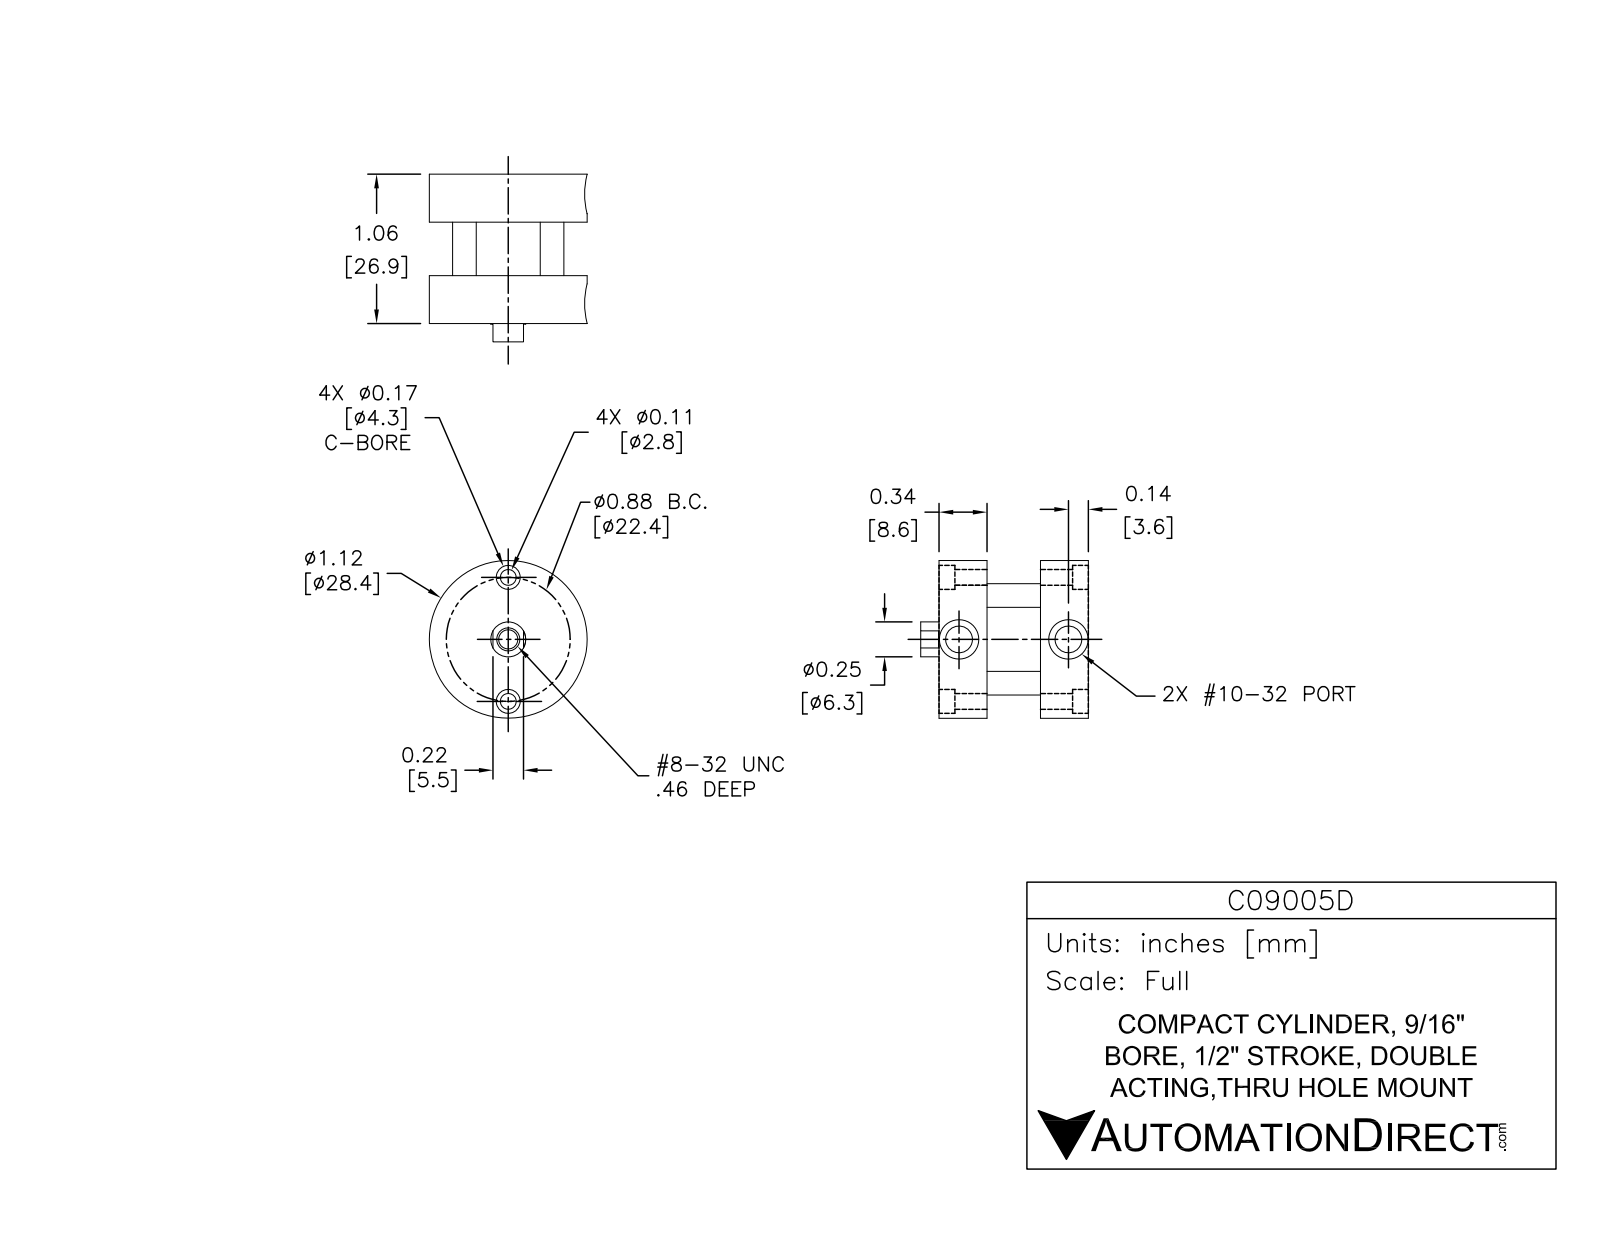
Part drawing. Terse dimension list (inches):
name: C09005D-FO1_BM_heads (2); C09005D-FO1_BM_tube; C09005D-FO1_BM_heads; C09005D-FO1_BM_r (+3 more)
written by: SolidWorks 2014 (AUTOMOTIVE_DESIGN)
unit: in
bodies: 9 solids, 145 faces (47 planar, 88 cylindrical, 10 other)
size: 1.19 × 1.12 × 1.12
volume: 0.713 in³; area: 13.56 in²
holes: 6× ⌀0.12, 2× ⌀0.156, 2× ⌀0.188, 1× ⌀0.134, 1× ⌀0.25, 1× ⌀0.252, 1× ⌀0.562, 1× ⌀0.61
bosses: 4× ⌀0.24, 1× ⌀1.12
rounds: 2× R0.156
face distances: 0.1, 0.48, 1.06, 0.72, 0.34, 0.34, 0.38, 0.72, 0.24, 0.82
hole spacings: 0.337, 0.44, 0.622, 0.813, 0.44, 0.88, 0.78, 0.88
